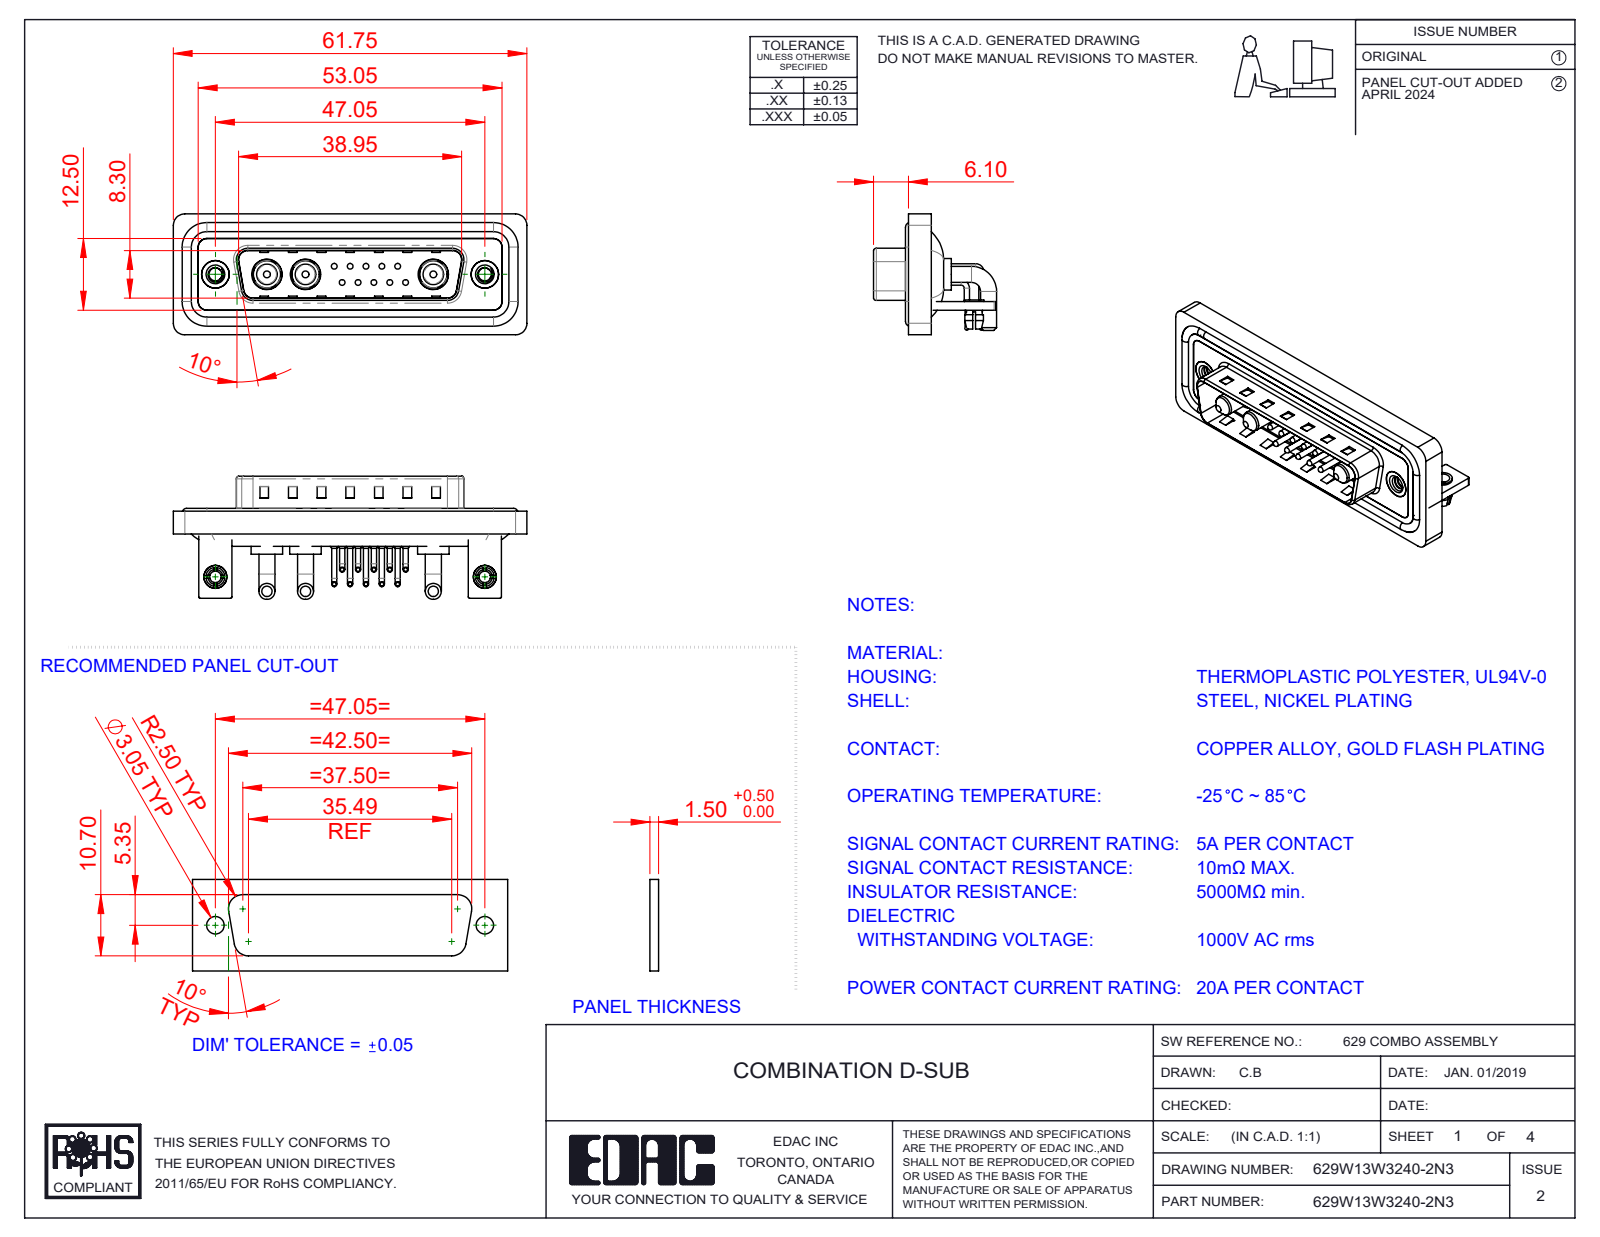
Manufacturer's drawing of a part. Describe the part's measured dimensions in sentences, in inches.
The part is named "629Combo Contact Row 2; 629Combo Stabilizer Bracket; 629Combo Shell Front_25 Contacts; 629Combo Board Lock (+7 more)". Its 3-D file was written by "SolidWorks 2023 (CONFIG_CONTROL_DESIGN)". It is 27 solids with 1844 faces: 947 planar, 661 cylindrical and 236 other. Overall it measures 2.431 by 0.846 by 0.831 inches. Its volume is 0.484 cubic inches and its surface area 20.6 square inches. Round holes: 12 of diameter 0.079, 10 of diameter 0.03, 10 of diameter 0.063, 3 of diameter 0.191, 3 of diameter 0.209, 2 of diameter 0.089, 2 of diameter 0.098, 2 of diameter 0.126, 2 of diameter 0.157, 2 of diameter 0.189, 2 of diameter 0.197. Round bosses or shafts: 20 of diameter 0.035, 10 of diameter 0.059, 10 of diameter 0.039, 10 of diameter 0.026, 6 of diameter 0.11, 4 of diameter 0.063, 3 of diameter 0.217, 3 of diameter 0.205. Partial cylindrical surfaces (rounded edges, fillets, slot ends): 19 of radius 0.079, 18 of radius 0.059, 16 of radius 0.01, 10 of radius 0.04, 9 of radius 0.02, 8 of radius 0.063, 4 of radius 0.024, 4 of radius 0.026. The main face-to-face distances are 0.016, 0.031, 0.059, 0.114, 0.083, 0.043, 0.161, 0.063, 0.146, 0.177. The hole center spacings are 0.124, 0.109, 0.198, 0.218, 0.295, 0.198, 0.327, 0.398.
